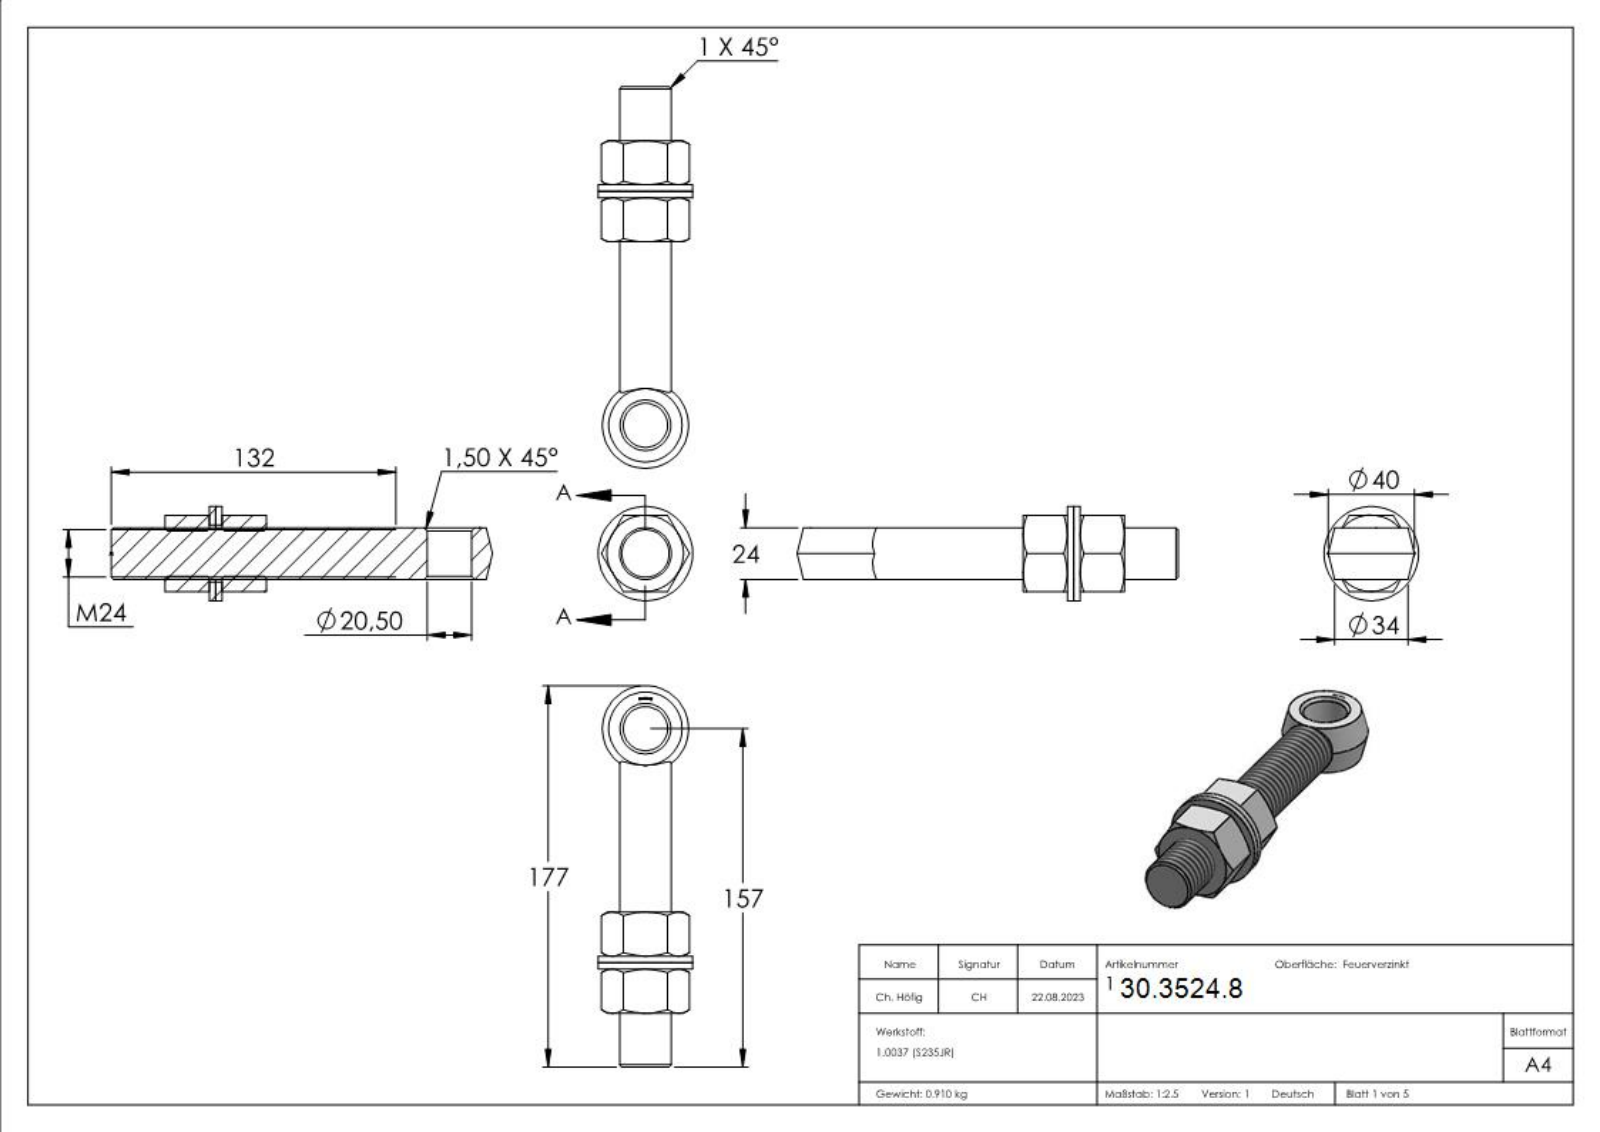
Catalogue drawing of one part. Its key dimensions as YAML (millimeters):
part_name: "121-Mxx-AS Teil3_121-M24-AS Teil3; 121-Mxx-AS Teil2_121-M24-AS Teil2; 121-Mxx-AS Teil1_121-M24-AS Teil3; 121-M24-AS"
step_written_by: "SolidWorks 2018 (CONFIG_CONTROL_DESIGN)"
units: millimeters
bodies: {solids: 5, faces: 174, planar: 106, cylindrical: 8, other: 60}
overall_size: [177, 43.8, 43.8]
volume: 116607
surface_area: 31528
round_holes:
  - {diameter: 20.5, count: 1}
  - {diameter: 21, count: 1}
  - {diameter: 26.3, count: 1}
round_bosses_or_shafts:
  - {diameter: 43.8, count: 1}
  - {diameter: 24, count: 1}
face_to_face_distances: [35.5, 3, 3.1, 6.1, 20.4, 23.4, 23.5, 26.5, 5.75, 29.75]
